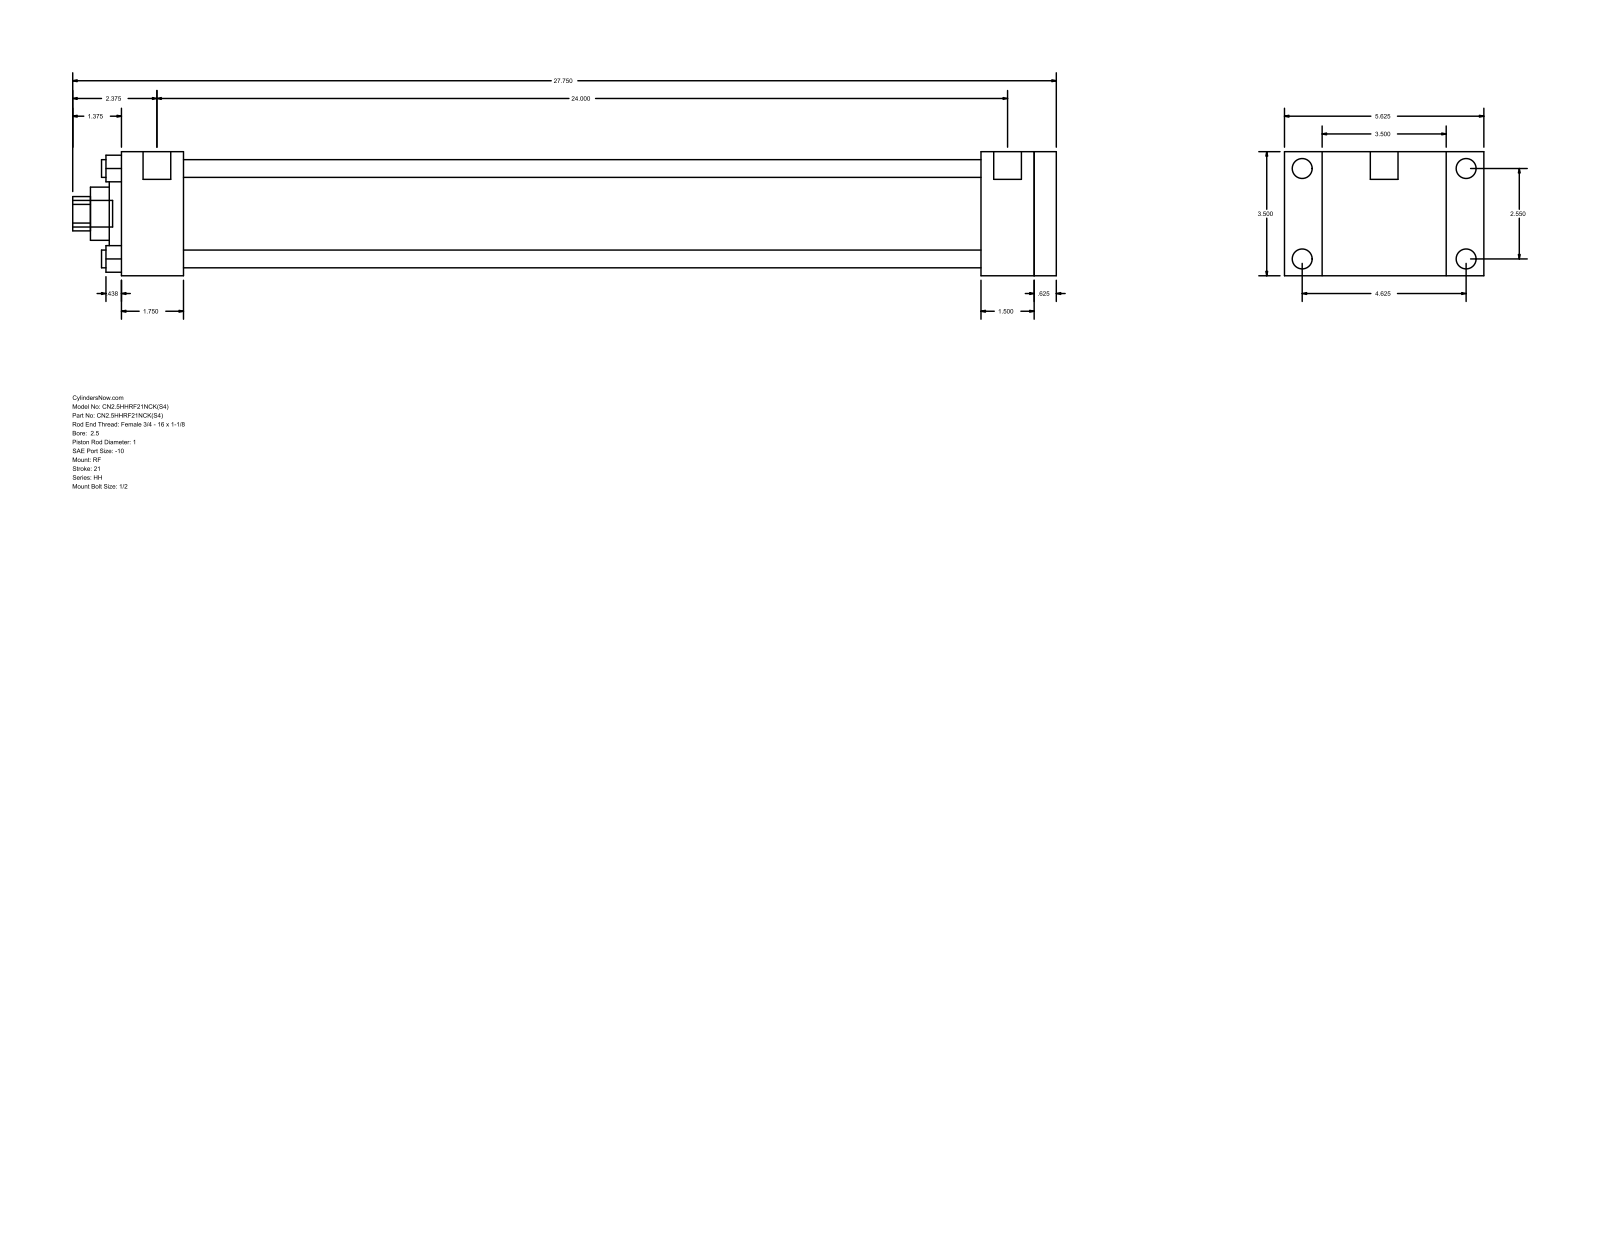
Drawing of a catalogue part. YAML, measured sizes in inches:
part_name: "HH_RF__0250_1"
step_written_by: "GSSL Pune (CONFIG_CONTROL_DESIGN)"
units: inches
bodies: {solids: 0, faces: 94, planar: 65, cylindrical: 29, other: 0}
overall_size: [27.75, 5.625, 3.5]
round_holes:
  - {diameter: 0.5, count: 4}
  - {diameter: 1, count: 1}
  - {diameter: 1.5, count: 1}
  - {diameter: 2.375, count: 1}
  - {diameter: 2.875, count: 1}
round_bosses_or_shafts:
  - {diameter: 0.563, count: 4}
  - {diameter: 0.219, count: 4}
  - {diameter: 0.781, count: 2}
  - {diameter: 0.75, count: 1}
partial_cylinders:
  - {radius: 0.484, count: 1}
face_to_face_distances: [3.5, 0.625, 25.75, 26.375, 1.75, 24, 24.625, 24.25, 22.5, 1.5]
hole_center_spacings: [1.803, 2.55, 3.606]
